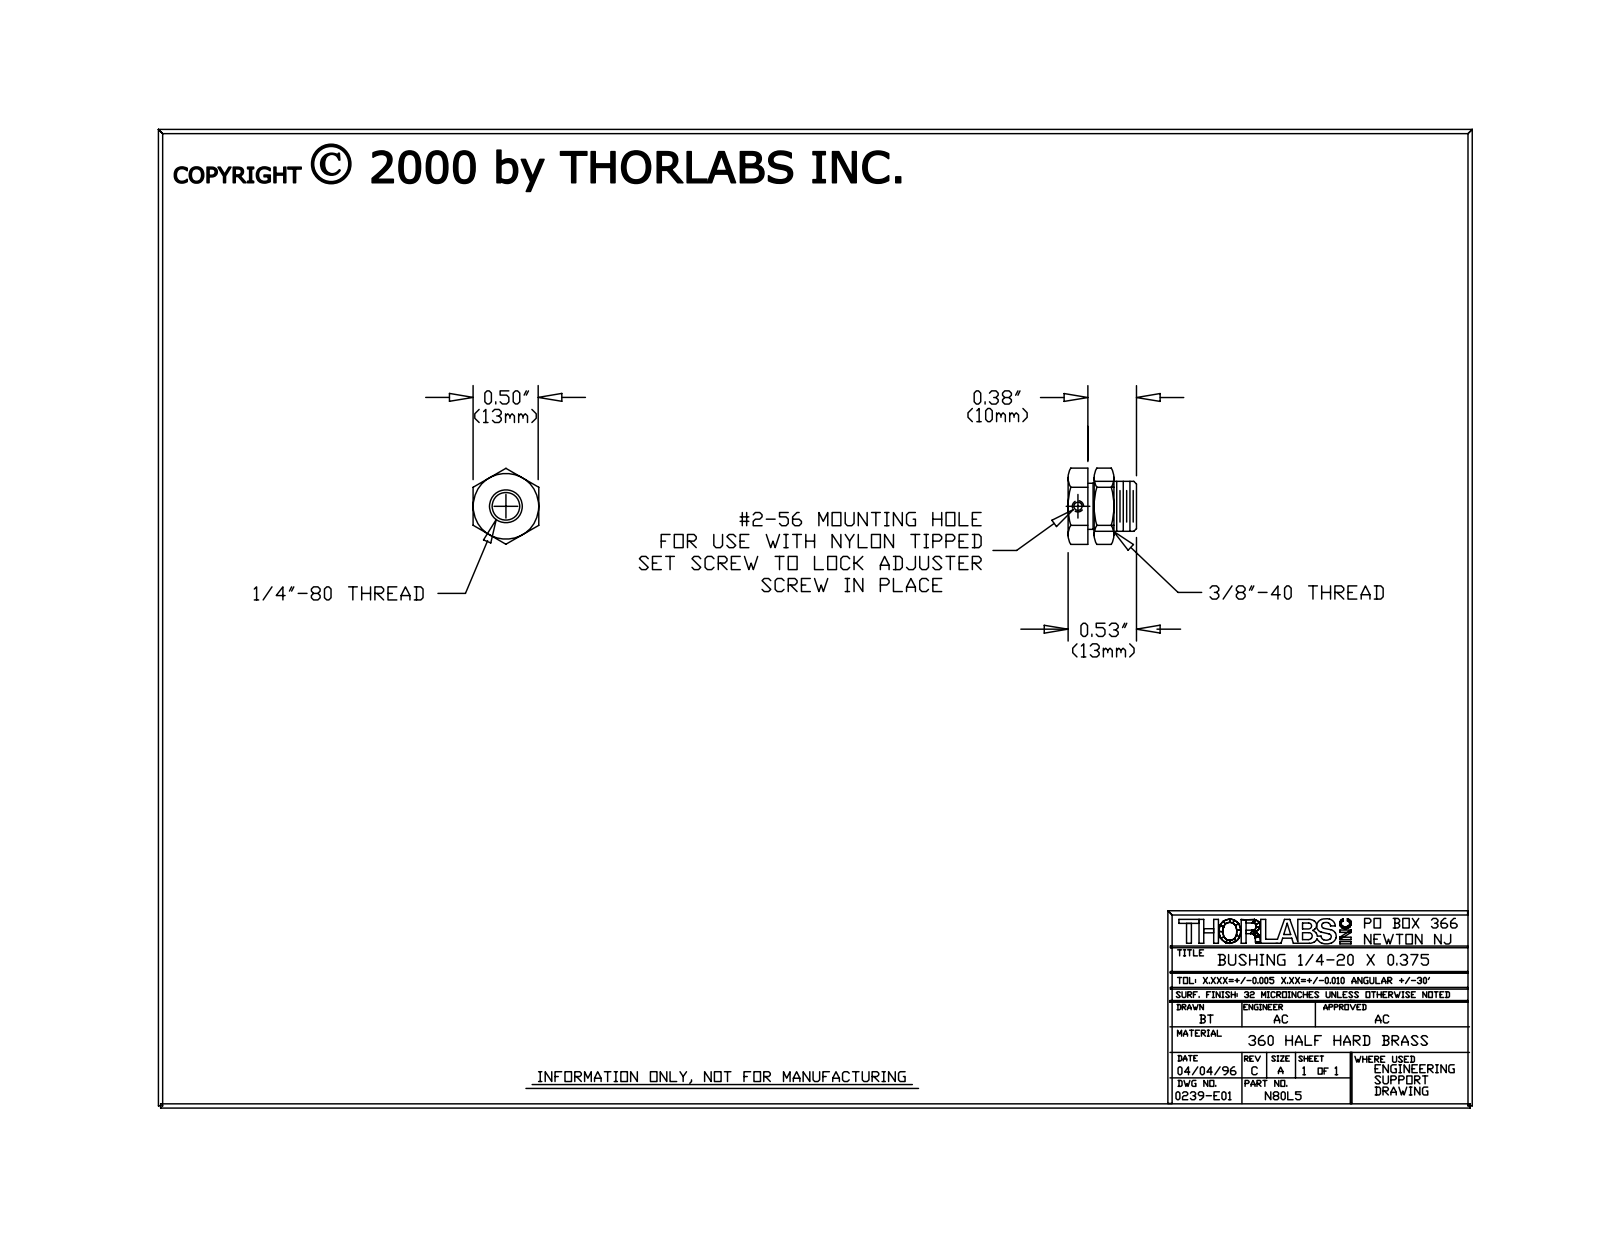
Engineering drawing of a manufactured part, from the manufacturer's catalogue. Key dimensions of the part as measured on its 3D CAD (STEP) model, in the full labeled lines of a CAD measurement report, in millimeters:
Part name (STEP PRODUCT): 0239-E0W
STEP written by: SolidWorks 2007 (AUTOMOTIVE_DESIGN)
Units: millimetres
Bodies: 3 solids, 65 faces (27 planar, 14 cylindrical, 24 other)
Overall size (bounding box): 14.7 × 13.3 × 12.7
Volume: 1 100 mm³ · Surface area: 1 335 mm²
Round holes (diameter × count): ⌀2.2 ×1, ⌀5.3 ×1, ⌀8.8 ×1
Round bosses / shafts (diameter × count): ⌀9.5 ×1, ⌀8.9 ×1, ⌀1.4 ×1
Main face-to-face distances: 12.7, 3.8, 3.2, 5.8, 9.7, 2.6, 6.5, 9.5, 3.7, 6.9
